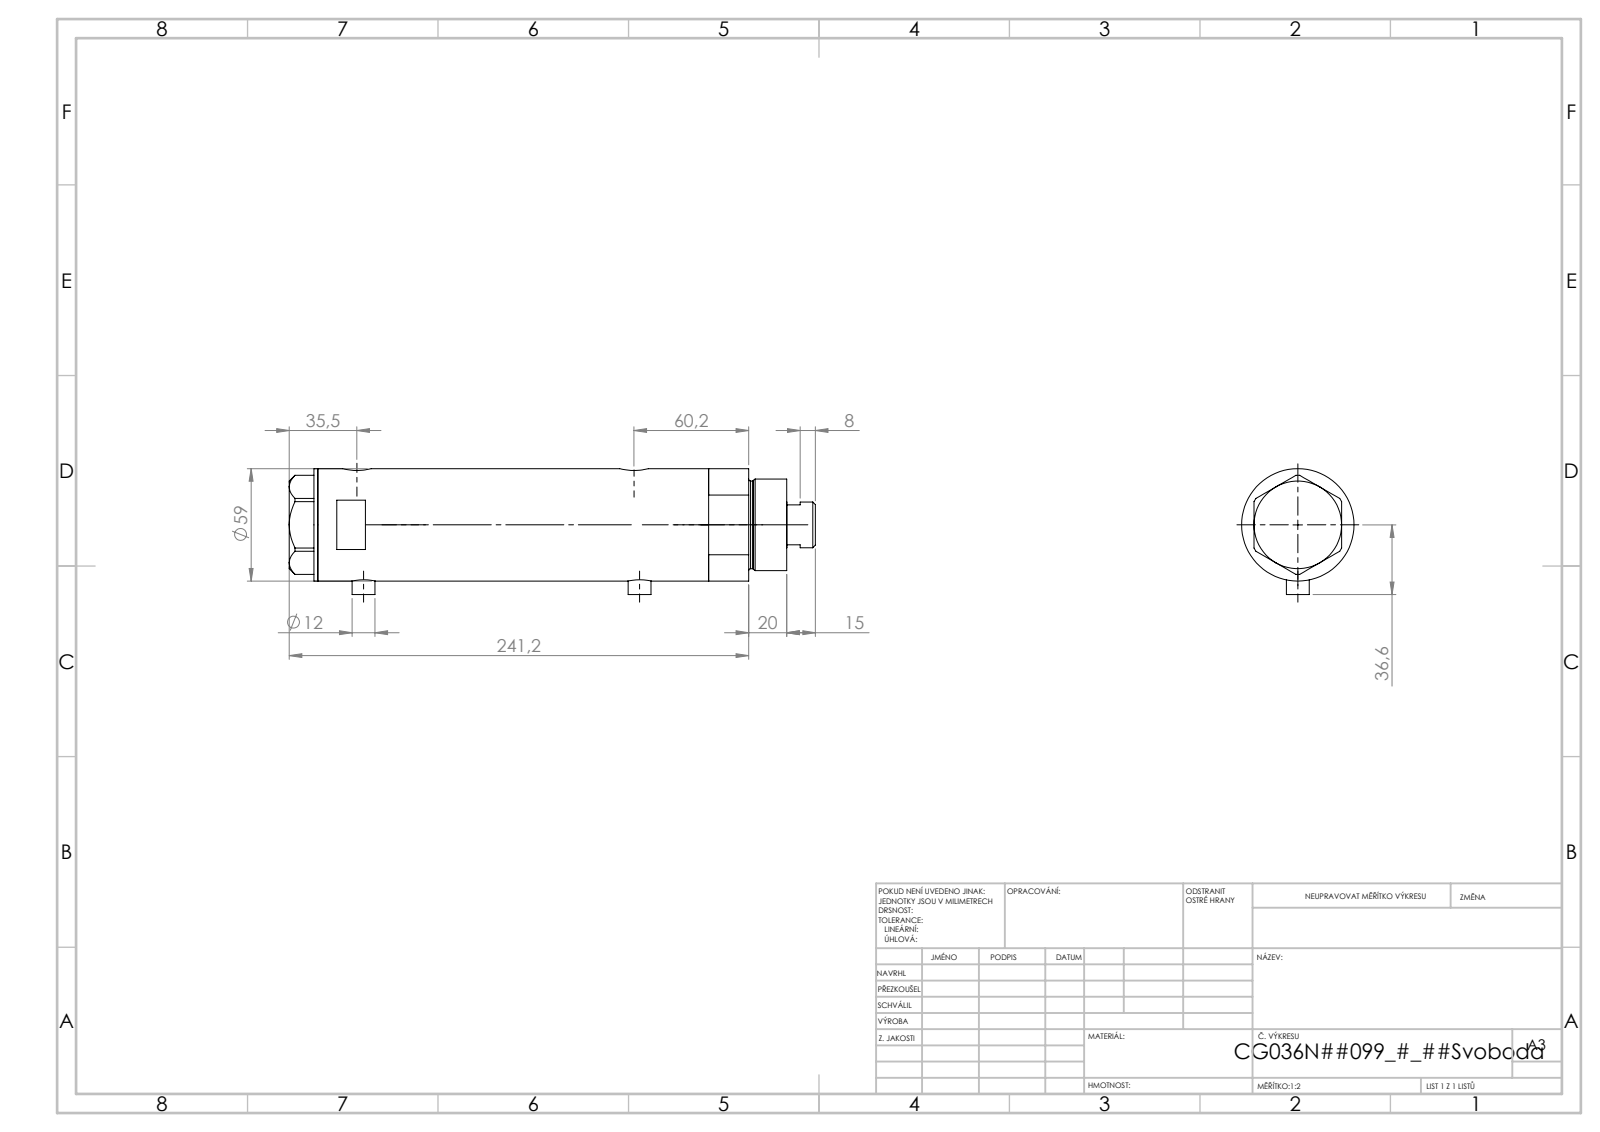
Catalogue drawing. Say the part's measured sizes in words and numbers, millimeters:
The part is named "V270CG_VC; V270CG_BACK; V270CG_MIDDLE; V270CG_FRONT". Its 3-D file was written by "SolidWorks 2019 (CONFIG_CONTROL_DESIGN)". It is 4 solids with 126 faces: 53 planar, 53 cylindrical and 20 other. Overall it measures 276.25 by 66.1 by 59 millimeters. Its volume is 629 803 cubic millimeters and its surface area 125 400 square millimeters. Round holes: 2 of diameter 5, 2 of diameter 9.73, 2 of diameter 12.5, 2 of diameter 15, 1 of diameter 8.5, 1 of diameter 25, 1 of diameter 26.5, 1 of diameter 36, 1 of diameter 40, 1 of diameter 52. Round bosses or shafts: 2 of diameter 12, 1 of diameter 59, 1 of diameter 48, 1 of diameter 46, 1 of diameter 24. The main face-to-face distances are 167.2, 23.5, 143.7, 15, 38.5, 182.2, 2, 246.2, 261.2, 222.7. The hole center spacings are 2.9, 3.5, 142, 144.9, 145.5, 148.4.
